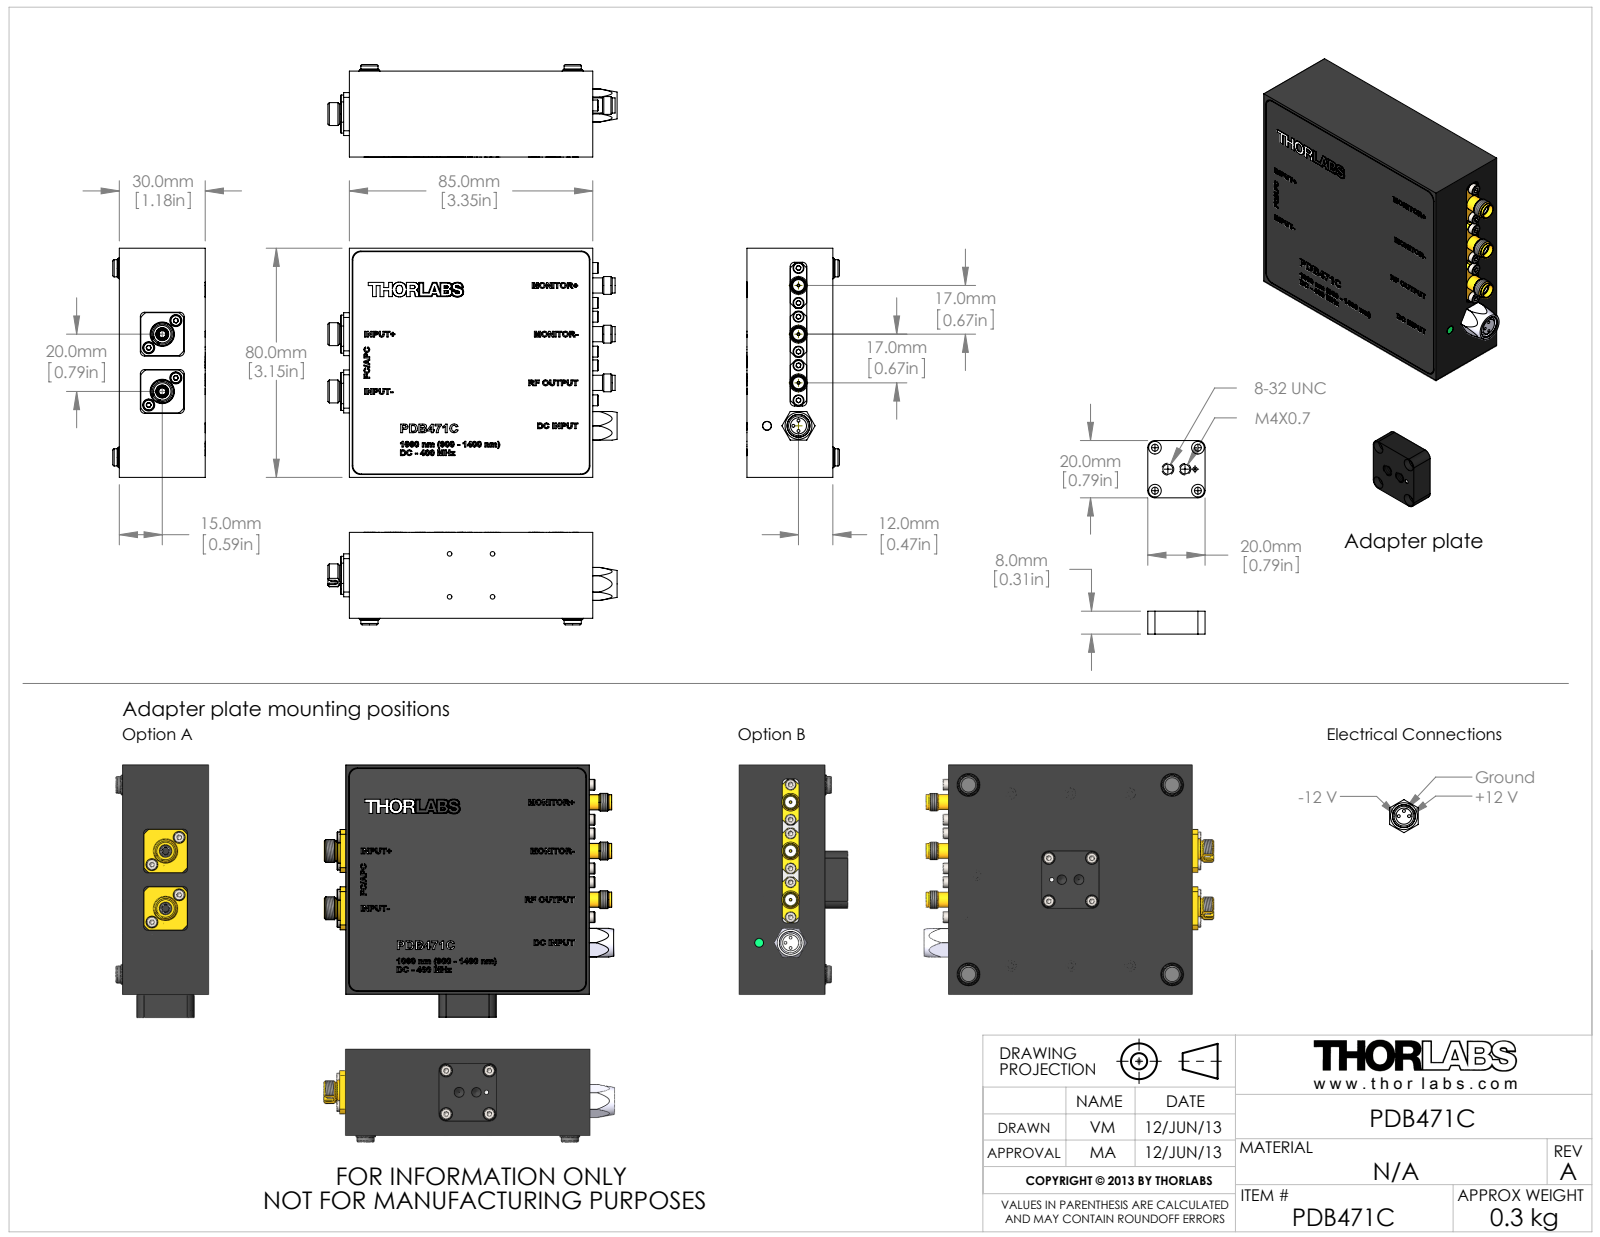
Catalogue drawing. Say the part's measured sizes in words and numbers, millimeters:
The part is named "M0075-22-0001 PDA10Bx (RKMF); FCAPCBuchse-03b-Senko switchable (Typ321-102); M0075-02-0032 SMABuchse (Rosenberger 32K722-500E3); M0092-0699 Grundkörper PDB480C-AC Rev C (+8 more)". Its 3-D file was written by "SolidWorks 2012 (AUTOMOTIVE_DESIGN)". It is 84 solids with 3089 faces: 1773 planar, 542 cylindrical and 774 other. Overall it measures 101 by 88 by 38 millimeters. Its volume is 89 116 cubic millimeters and its surface area 58 103 square millimeters. Round holes: 29 of diameter 1.6, 8 of diameter 2.4, 8 of diameter 4.4, 7 of diameter 8, 6 of diameter 2.6, 4 of diameter 1.5, 3 of diameter 0.8, 3 of diameter 1, 3 of diameter 4.1, 3 of diameter 4.2, 3 of diameter 4.7, 2 of diameter 3.2. Round bosses or shafts: 25 of diameter 3.8, 25 of diameter 2, 8 of diameter 4.2, 8 of diameter 2.3, 6 of diameter 6, 4 of diameter 1.57, 3 of diameter 6.22, 3 of diameter 5.3. Partial cylindrical surfaces (rounded edges, fillets, slot ends): 12 of radius 1.5, 12 of radius 3, 10 of radius 5, 8 of radius 2.5, 4 of radius 1.02, 3 of radius 8, 2 of radius 9.5, 1 of radius 5.75. The main face-to-face distances are 30, 29.7, 6, 23.7, 24, 5.5, 80, 85, 2, 74.5. The hole center spacings are 15, 8.75, 12.9, 6.1, 17, 2.83, 7.57, 10.9.
